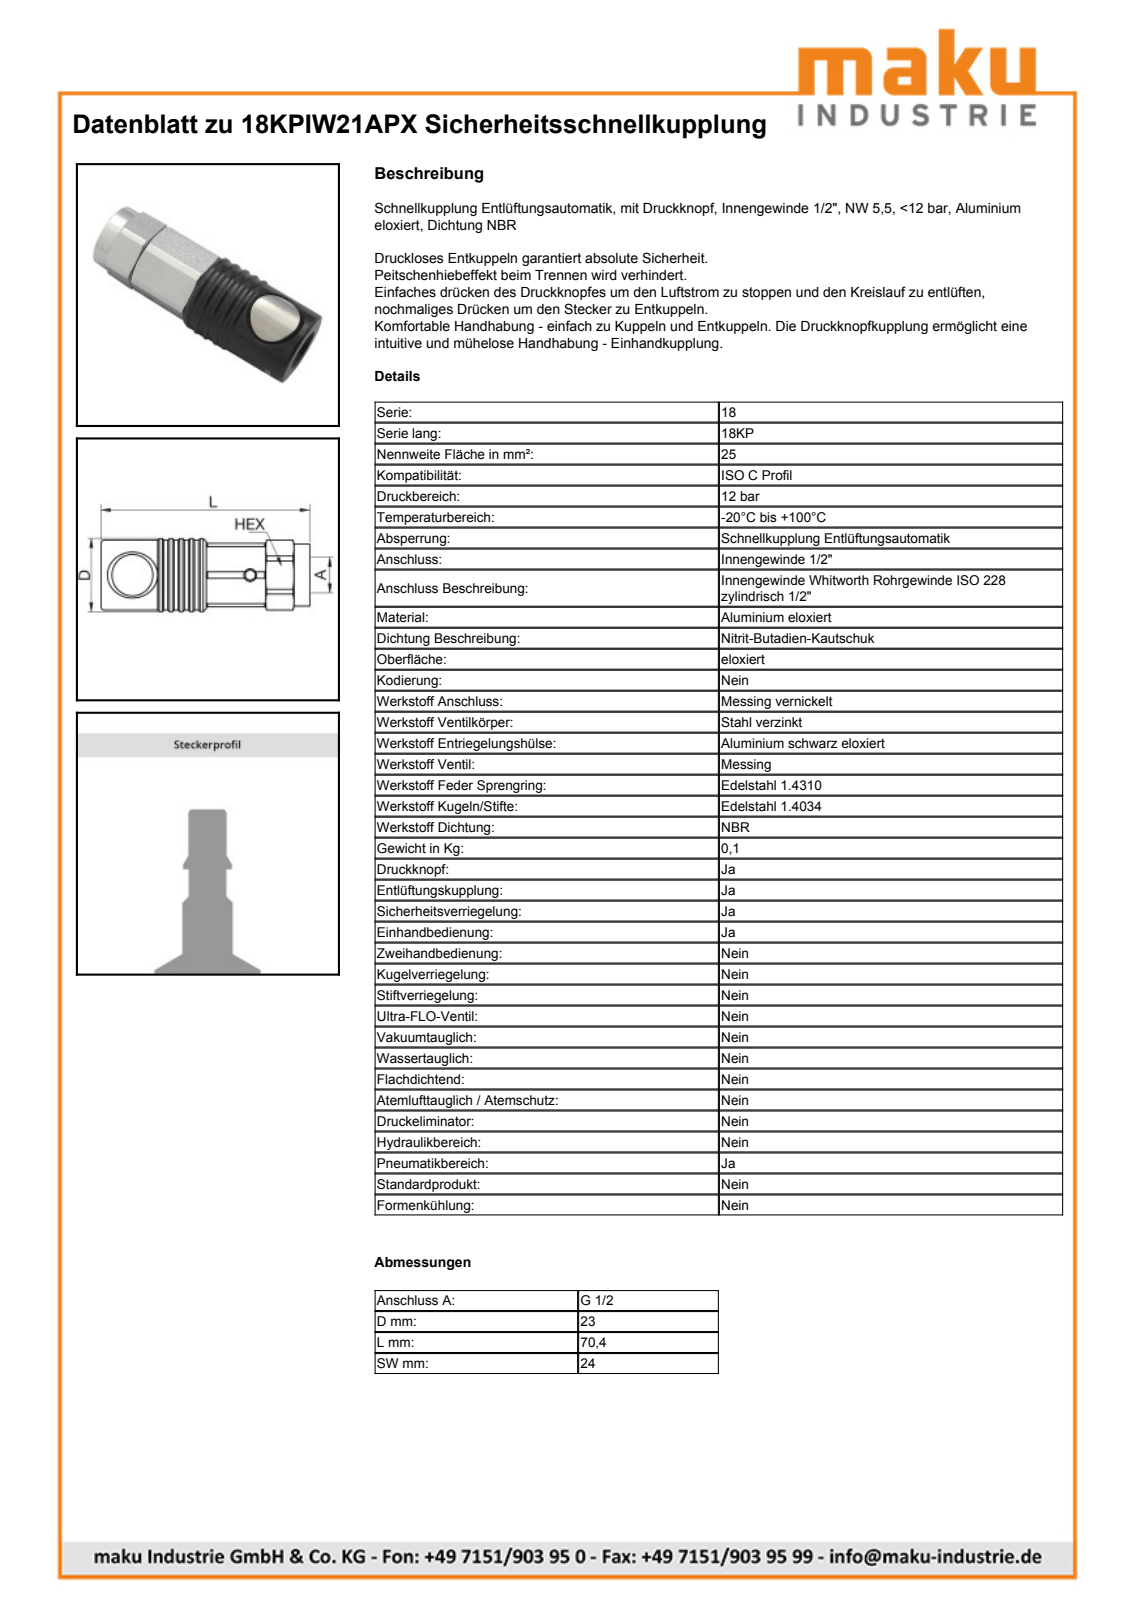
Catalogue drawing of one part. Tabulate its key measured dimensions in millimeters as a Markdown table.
| quantity | value |
| --- | --- |
| part name | 18KPIW21APX |
| STEP written by | Autodesk Inventor 2019 (CONFIG_CONTROL_DESIGN) |
| units | millimeters |
| bodies | 27 solids, 295 faces (94 planar, 106 cylindrical, 95 other) |
| overall size | 70.4 × 24.7 × 24 |
| volume | 28 004 mm³ |
| surface area | 20 620 mm² |
| round holes (diameter × count) | 2.5 × 1, 3.5 × 1, 5.5 × 1, 7 × 1, 8.5 × 1, 10.1 × 1, 10.4 × 1, 10.5 × 1, 11.1 × 1, 12.9 × 1, 14.05 × 1, 16 × 1 |
| round bosses / shafts (diameter × count) | 23.7 × 1, 23 × 1, 22 × 1, 20 × 1, 18.5 × 1, 18.2 × 1, 18 × 1, 16.95 × 1 |
| partial cylindrical surfaces (radius × count) | 3.77 × 1, 7.22 × 1, 7.8 × 1, 11 × 1, 12.35 × 1, 12.36 × 1 |
| main face-to-face distances | 20, 29.4, 52.4, 23, 11, 2, 22, 19, 18, 4.5 |
| hole center spacings | 1.2, 1.25, 37.43 |
